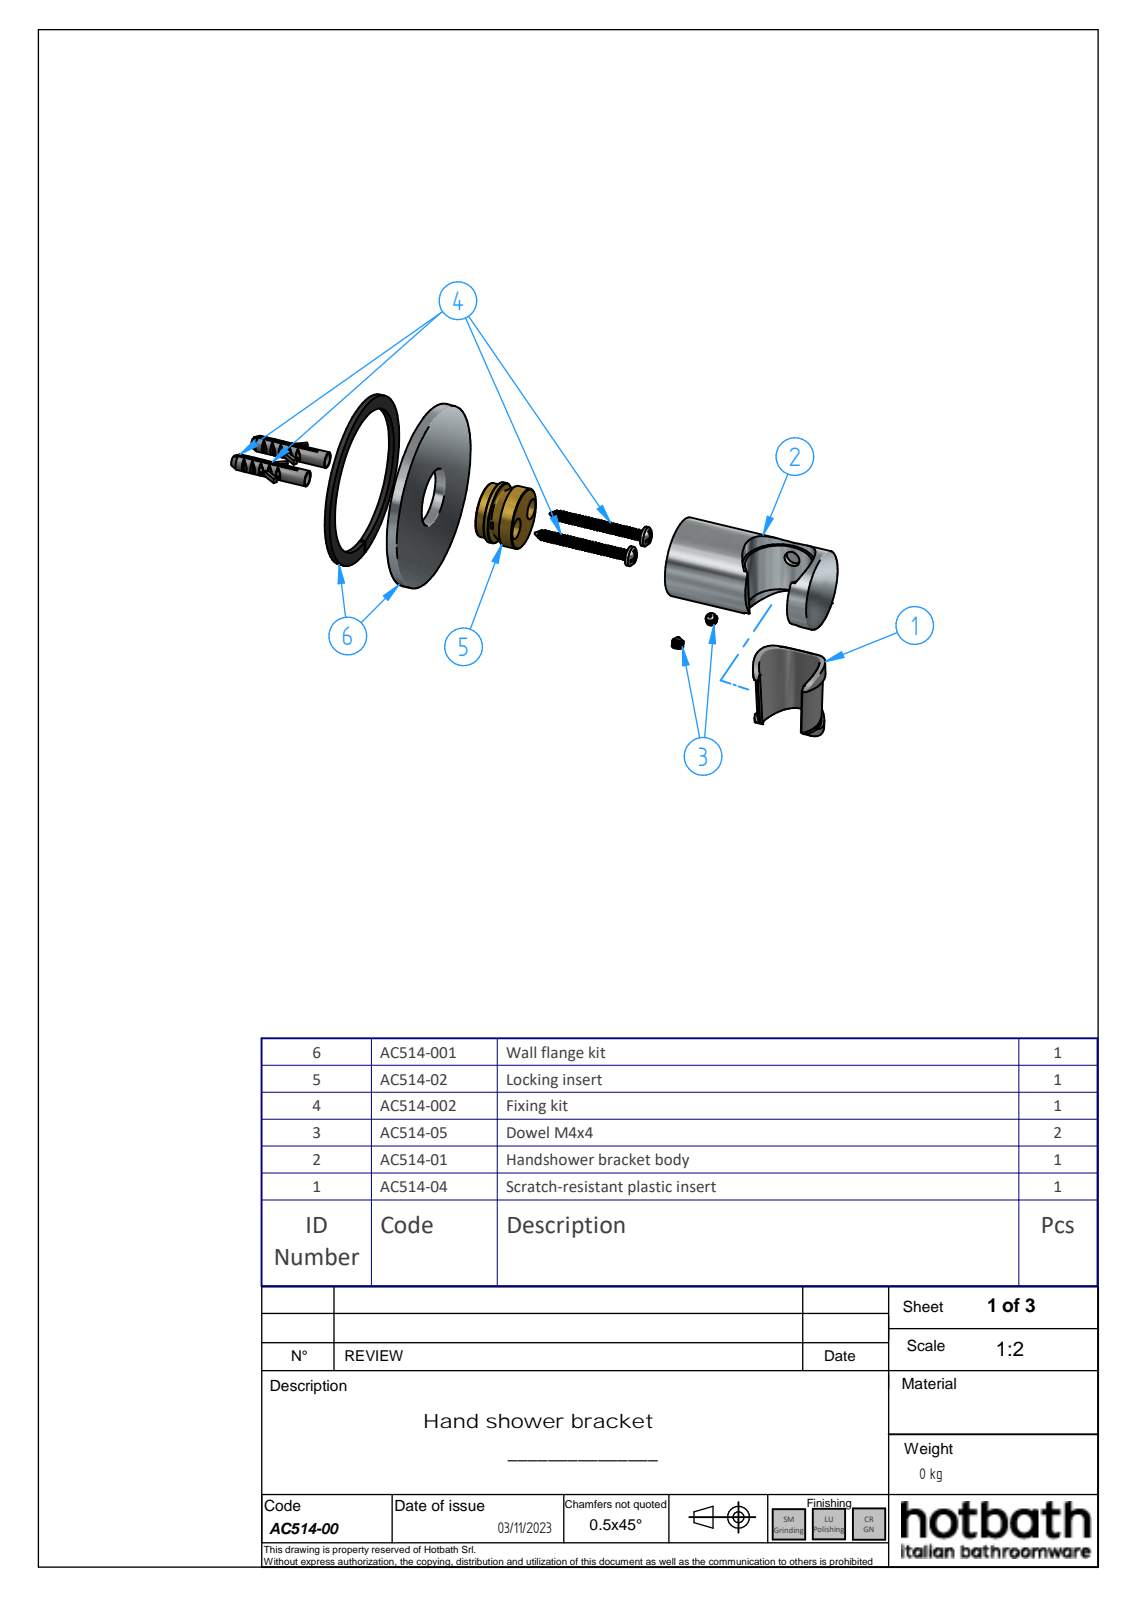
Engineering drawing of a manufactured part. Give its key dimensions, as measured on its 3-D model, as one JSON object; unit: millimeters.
{"part_name": "AC514-00; AC514-01; AC514-04; AC514-05 (+2 more)", "step_written_by": "Solid Edge (AUTOMOTIVE_DESIGN)", "units": "millimeters", "bodies": {"solids": 5, "faces": 231, "planar": 67, "cylindrical": 54, "other": 110}, "overall_size": [69.69, 69.69, 61], "volume_mm3": 35298, "surface_area_mm2": 20351, "round_holes": [[3.2, 2], [6, 1], [21.8, 1], [23.2, 1]], "round_bosses_or_shafts": [[4, 2], [30, 1]], "partial_cylinders_radius": [[0.15, 14], [0.3, 6], [0.5, 6], [0.52, 2], [1, 2], [12, 1], [13.1, 1], [13.6, 1]], "face_to_face_distances": [4, 1, 3, 2.5, 0.5, 1.5, 57, 59.5, 60, 61]}
